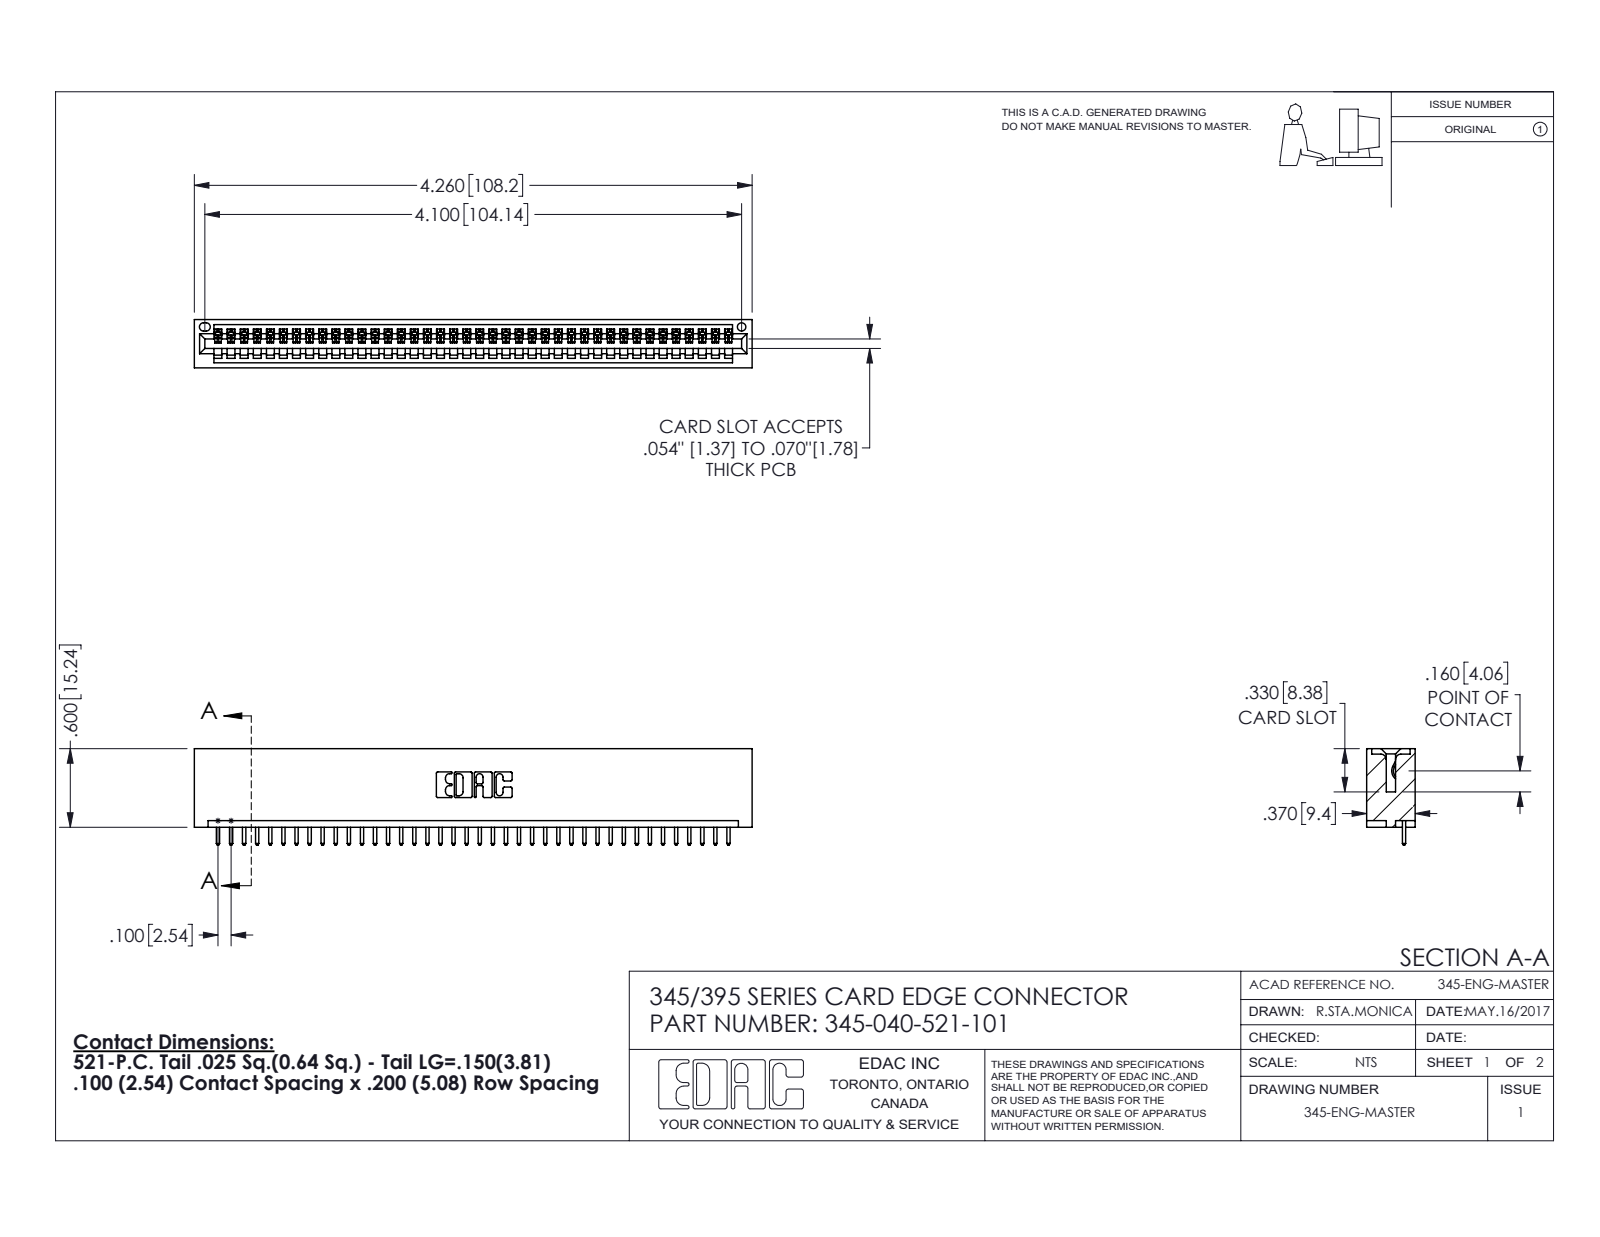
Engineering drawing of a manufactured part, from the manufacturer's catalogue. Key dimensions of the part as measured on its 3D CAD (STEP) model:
Part name (STEP PRODUCT): 345-292-001_345-293-121; 345 Part_No Mounting Lugs; 345-040-521-101
STEP written by: SolidWorks 2016 (CONFIG_CONTROL_DESIGN)
Units: inches
Bodies: 41 solids, 2438 faces (1676 planar, 762 cylindrical, 0 other)
Overall size (bounding box): 4.26 × 0.737 × 0.37
Volume: 0.655 in³ · Surface area: 21.67 in²
Round holes (diameter × count): ⌀0.064 ×1
Partial cylindrical surfaces — rounded edges, fillets, slot ends (radius × count): R0.006 ×80, R0.01 ×80, R0.01 ×22, R0.007 ×6, R0.031 ×6, R0.026 ×3, R0.031 ×2, R0.04 ×2
Main face-to-face distances: 0.298, 0.072, 0.37, 0.2, 0.098, 0.272, 0.025, 0.225, 0.149, 0.072
